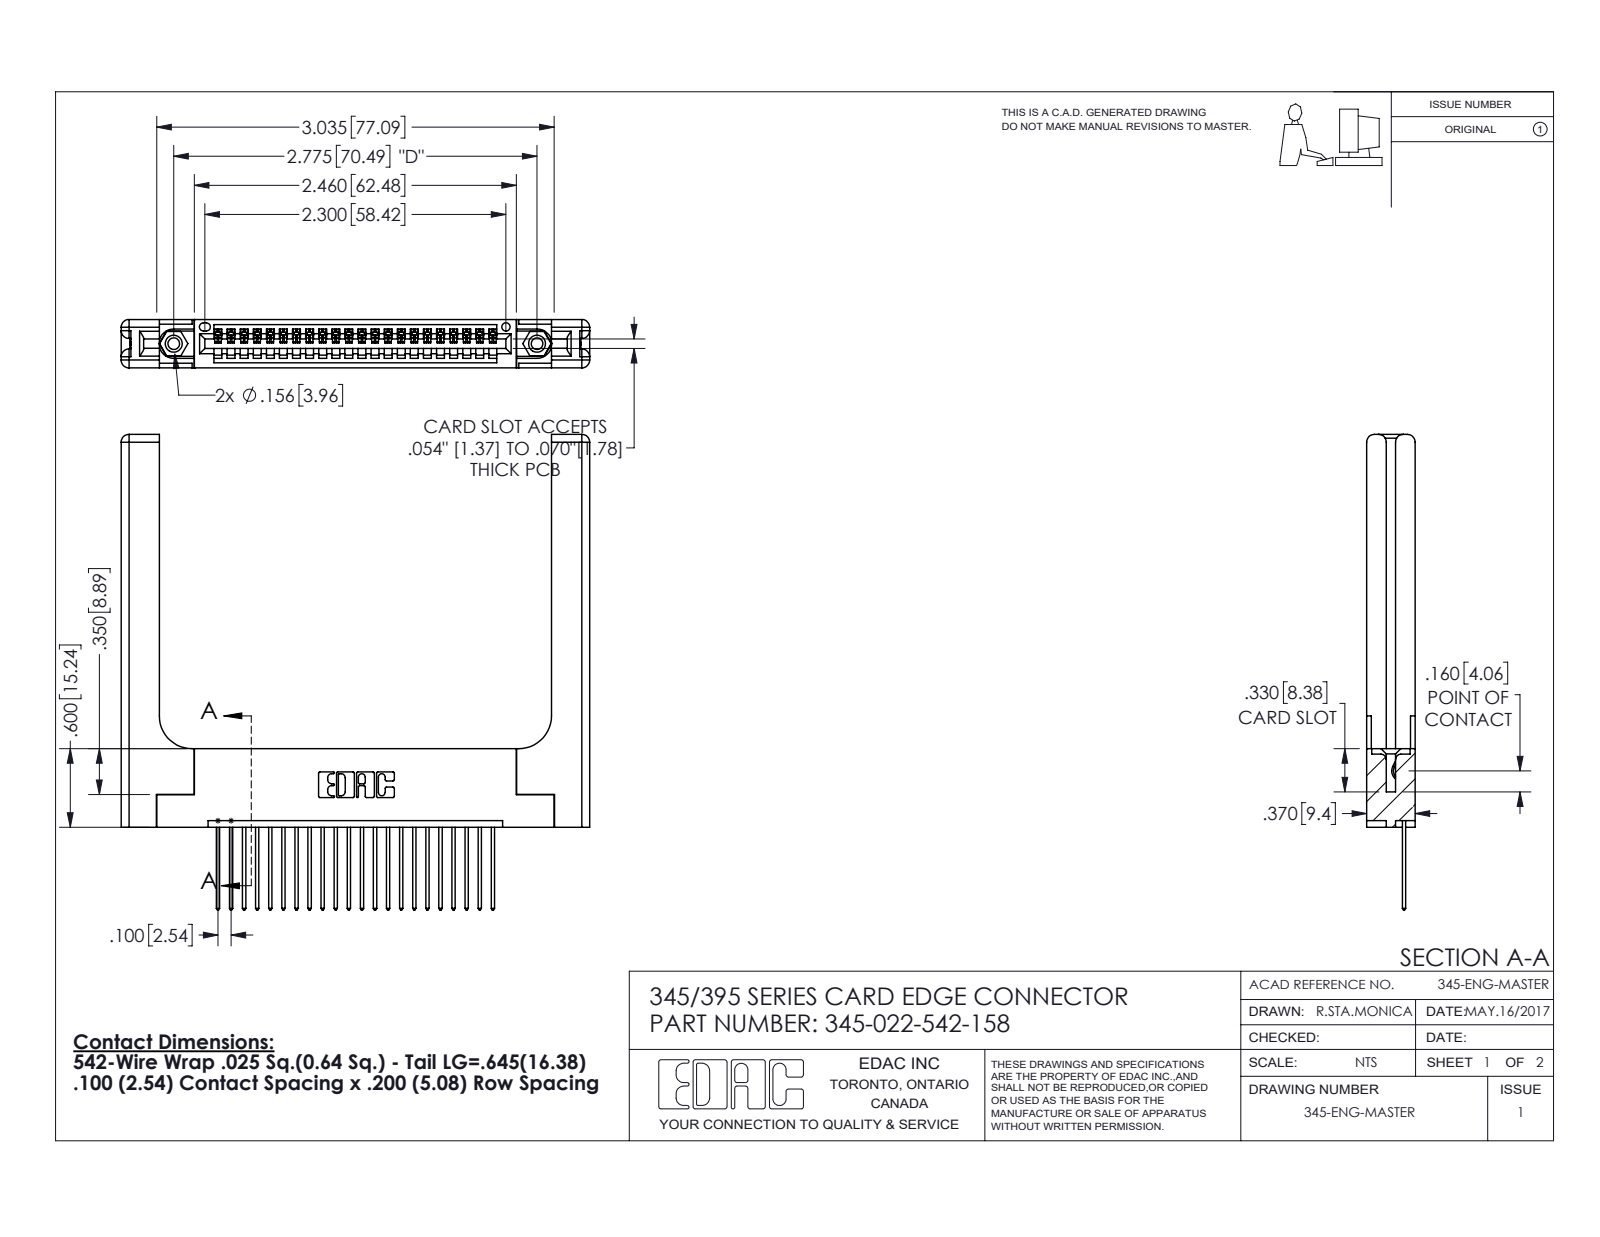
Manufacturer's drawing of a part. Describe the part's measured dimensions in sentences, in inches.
The part is named "345-292-001_345-293-142; 345-022-542-158; 345 Part_Flush Mounting Lugs - 0.156 Dia-TH; 345-220-058_345-220-058 (+1 more)". Its 3-D file was written by "SolidWorks 2016 (CONFIG_CONTROL_DESIGN)". It is 27 solids with 1658 faces: 1108 planar, 490 cylindrical and 60 other. Overall it measures 3.632 by 3.579 by 0.37 inches. Its volume is 1.039 cubic inches and its surface area 25.83 square inches. Round holes: 2 of diameter 0.089, 2 of diameter 0.125, 2 of diameter 0.156, 1 of diameter 0.064. Round bosses or shafts: 2 of diameter 0.155. Partial cylindrical surfaces (rounded edges, fillets, slot ends): 44 of radius 0.006, 44 of radius 0.01, 22 of radius 0.01, 16 of radius 0.06, 6 of radius 0.007, 6 of radius 0.031, 3 of radius 0.026, 2 of radius 0.03. The main face-to-face distances are 0.37, 0.072, 0.298, 0.2, 0.15, 0.148, 0.098, 0.272, 0.025, 0.077. The hole center spacings are 0.27, 2.541, 2.775.
